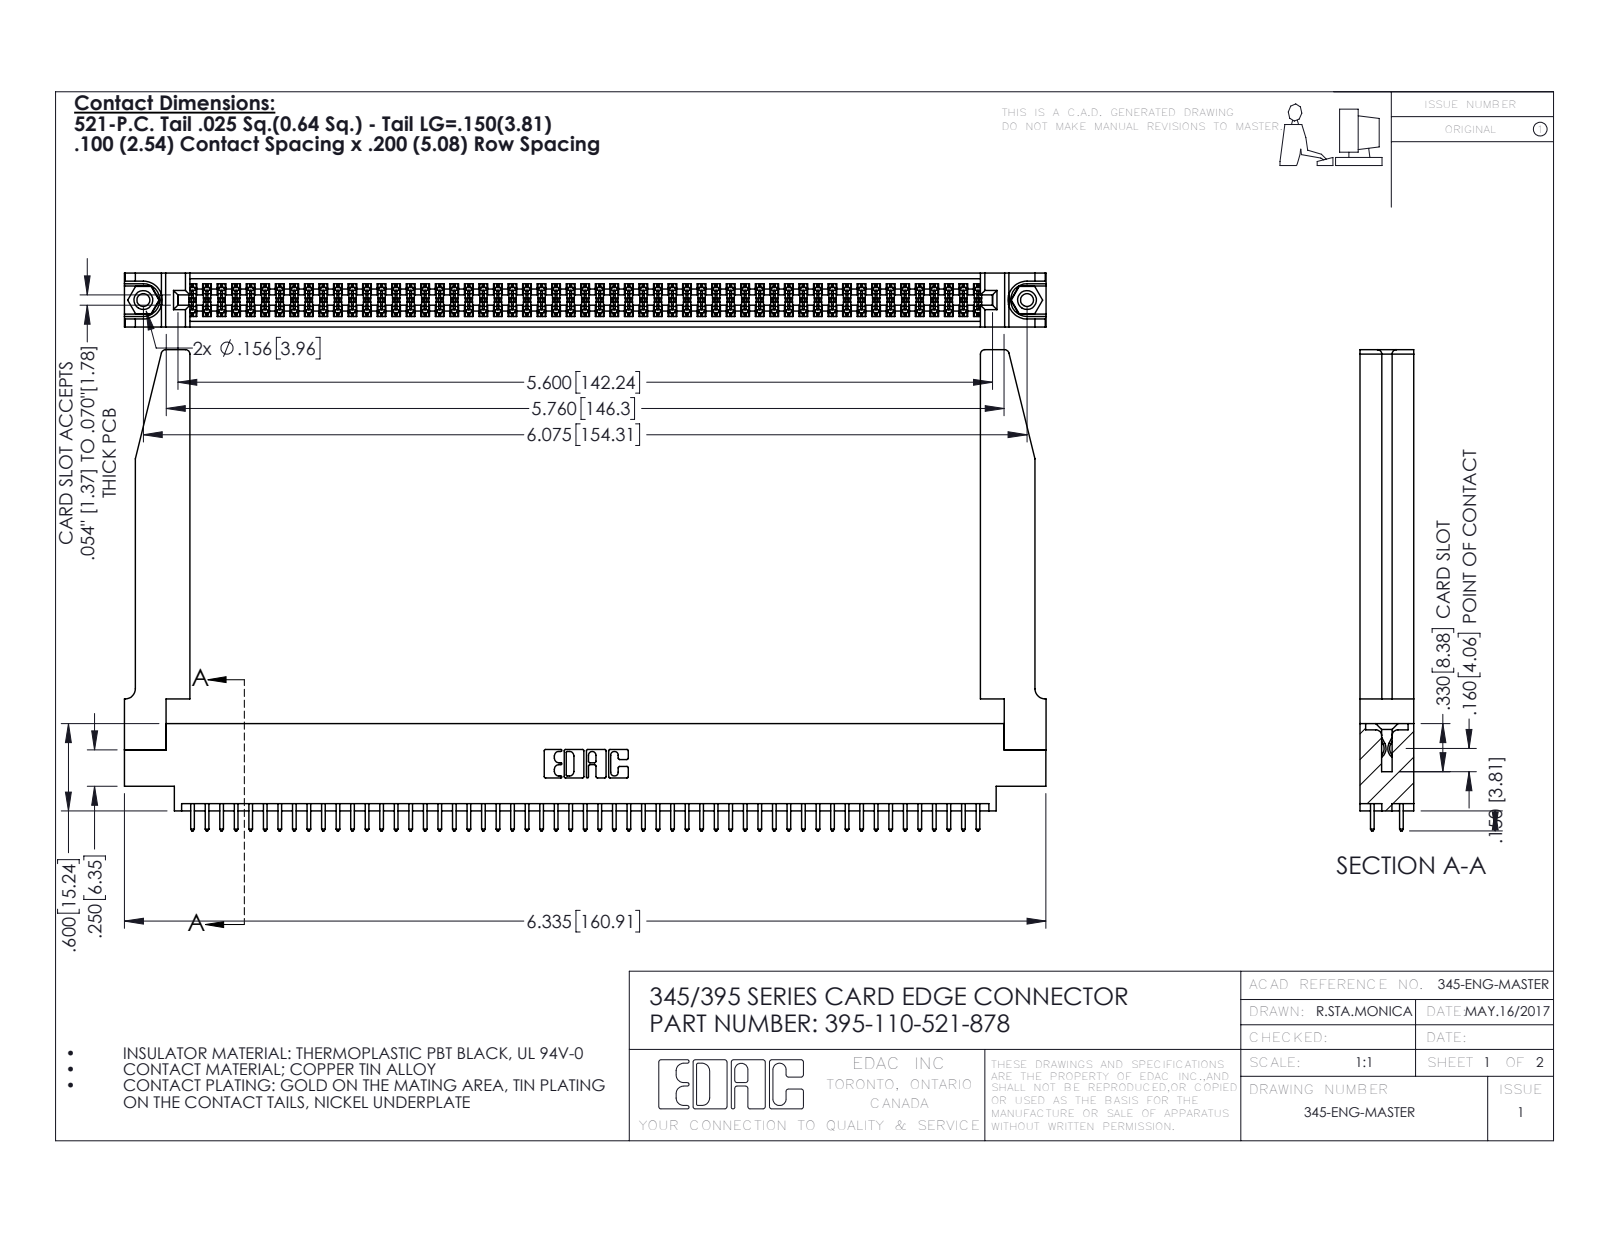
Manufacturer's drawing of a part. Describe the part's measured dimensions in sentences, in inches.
The part is named "345 Part_0.170 Offset - 0.156 Dia-TH; 345-250-001_345-250-001-102; 345-220-078_345-220-078; 345-292-001_345-293-121 (+1 more)". Its 3-D file was written by "SolidWorks 2016 (CONFIG_CONTROL_DESIGN)". It is 115 solids with 5864 faces: 3856 planar, 1956 cylindrical and 52 other. Overall it measures 6.336 by 3.307 by 0.37 inches. Its volume is 1.426 cubic inches and its surface area 46.49 square inches. Round holes: 2 of diameter 0.089, 2 of diameter 0.125, 2 of diameter 0.156, 1 of diameter 0.064. Round bosses or shafts: 2 of diameter 0.155. Partial cylindrical surfaces (rounded edges, fillets, slot ends): 165 of radius 0.006, 110 of radius 0.01, 22 of radius 0.01, 8 of radius 0.03, 6 of radius 0.007, 6 of radius 0.031, 3 of radius 0.026, 2 of radius 0.014. The main face-to-face distances are 0.072, 0.37, 0.298, 0.098, 0.272, 0.025, 0.2, 0.225, 0.175, 0.148. The hole center spacings are 0.27, 5.839, 6.075.
